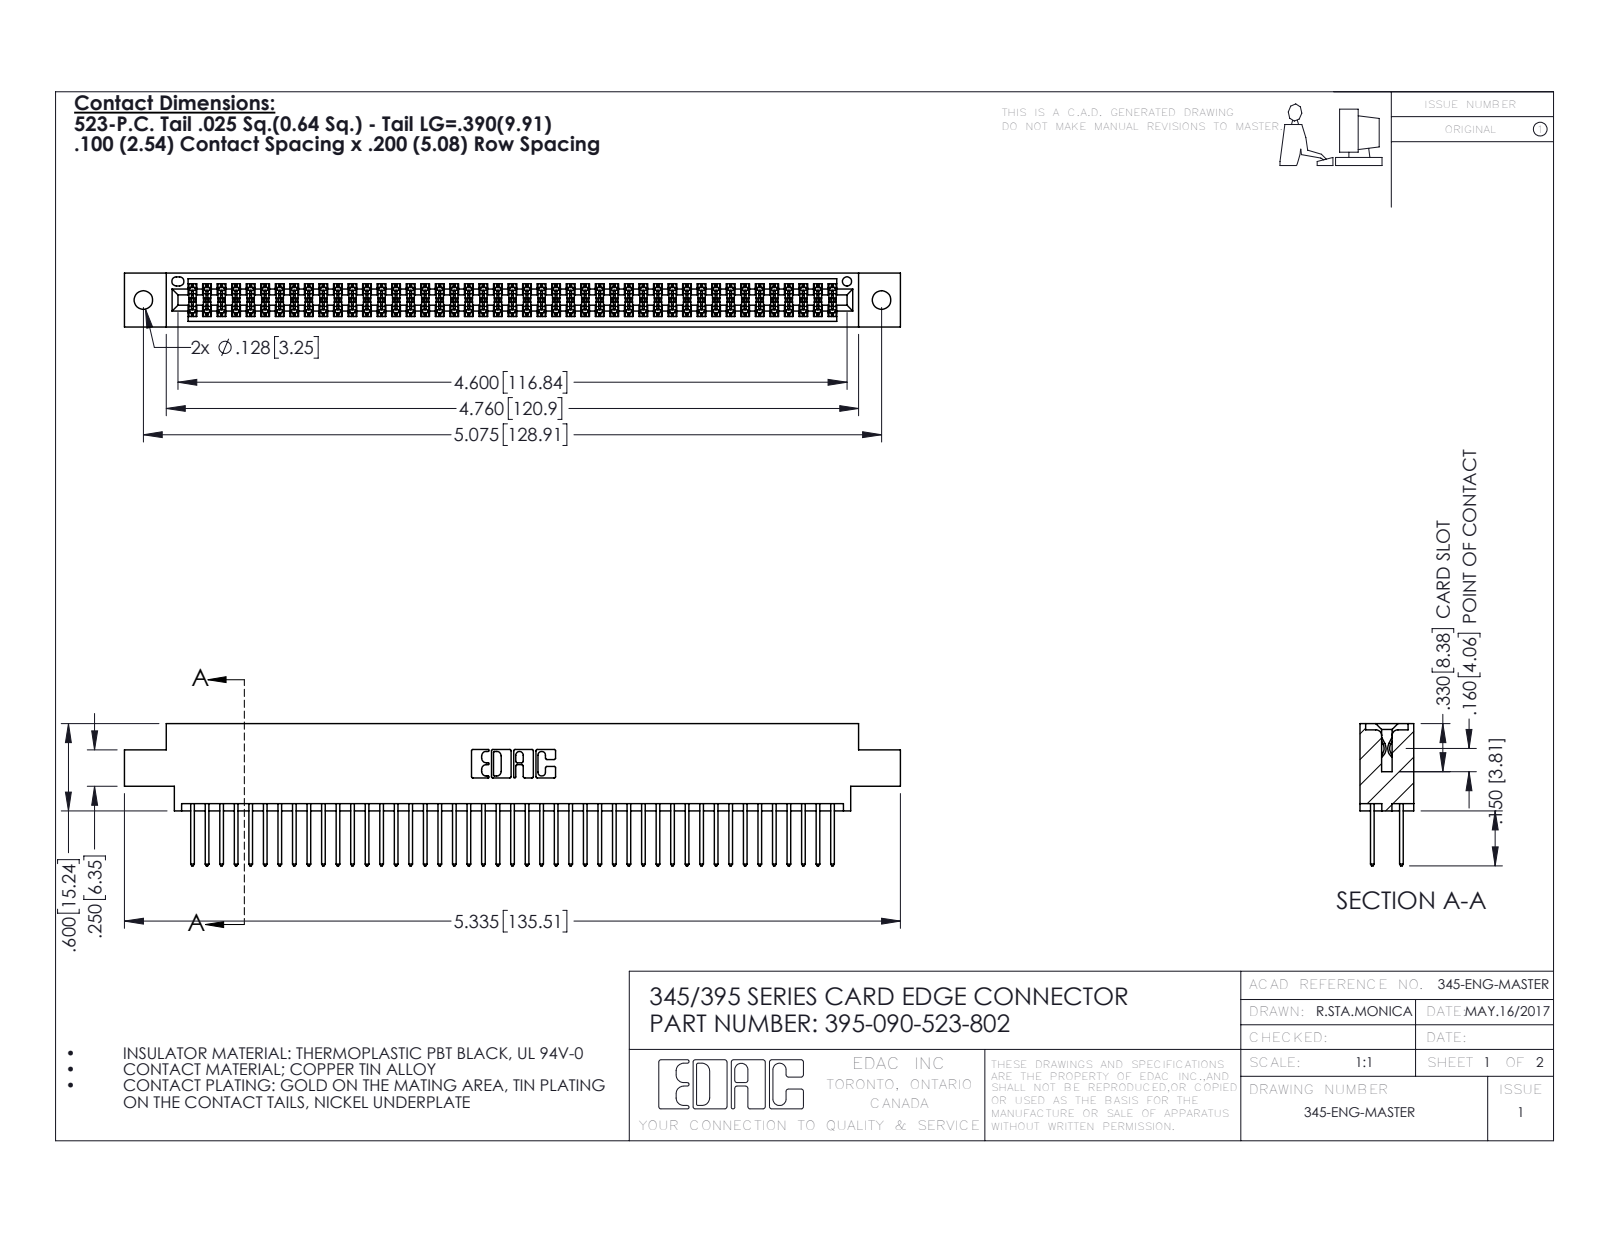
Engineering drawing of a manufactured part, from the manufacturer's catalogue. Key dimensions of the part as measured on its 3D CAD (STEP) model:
Part name (STEP PRODUCT): 345 Part_0.170 Offset - 0.128 Dia; 395-090-523-802; 345-292-001_345-293-123
STEP written by: SolidWorks 2016 (CONFIG_CONTROL_DESIGN)
Units: inches
Bodies: 91 solids, 4630 faces (3054 planar, 1576 cylindrical, 0 other)
Overall size (bounding box): 5.335 × 0.977 × 0.37
Volume: 0.807 in³ · Surface area: 31.47 in²
Round holes (diameter × count): ⌀0.128 ×2, ⌀0.064 ×1
Partial cylindrical surfaces — rounded edges, fillets, slot ends (radius × count): R0.006 ×135, R0.01 ×90, R0.01 ×22, R0.007 ×6, R0.031 ×6, R0.026 ×3, R0.014 ×2, R0.019 ×2
Main face-to-face distances: 0.298, 0.072, 0.2, 0.098, 0.272, 0.025, 0.37, 0.225, 0.175, 0.149
Hole centre spacings: 0.27, 4.839, 5.075
